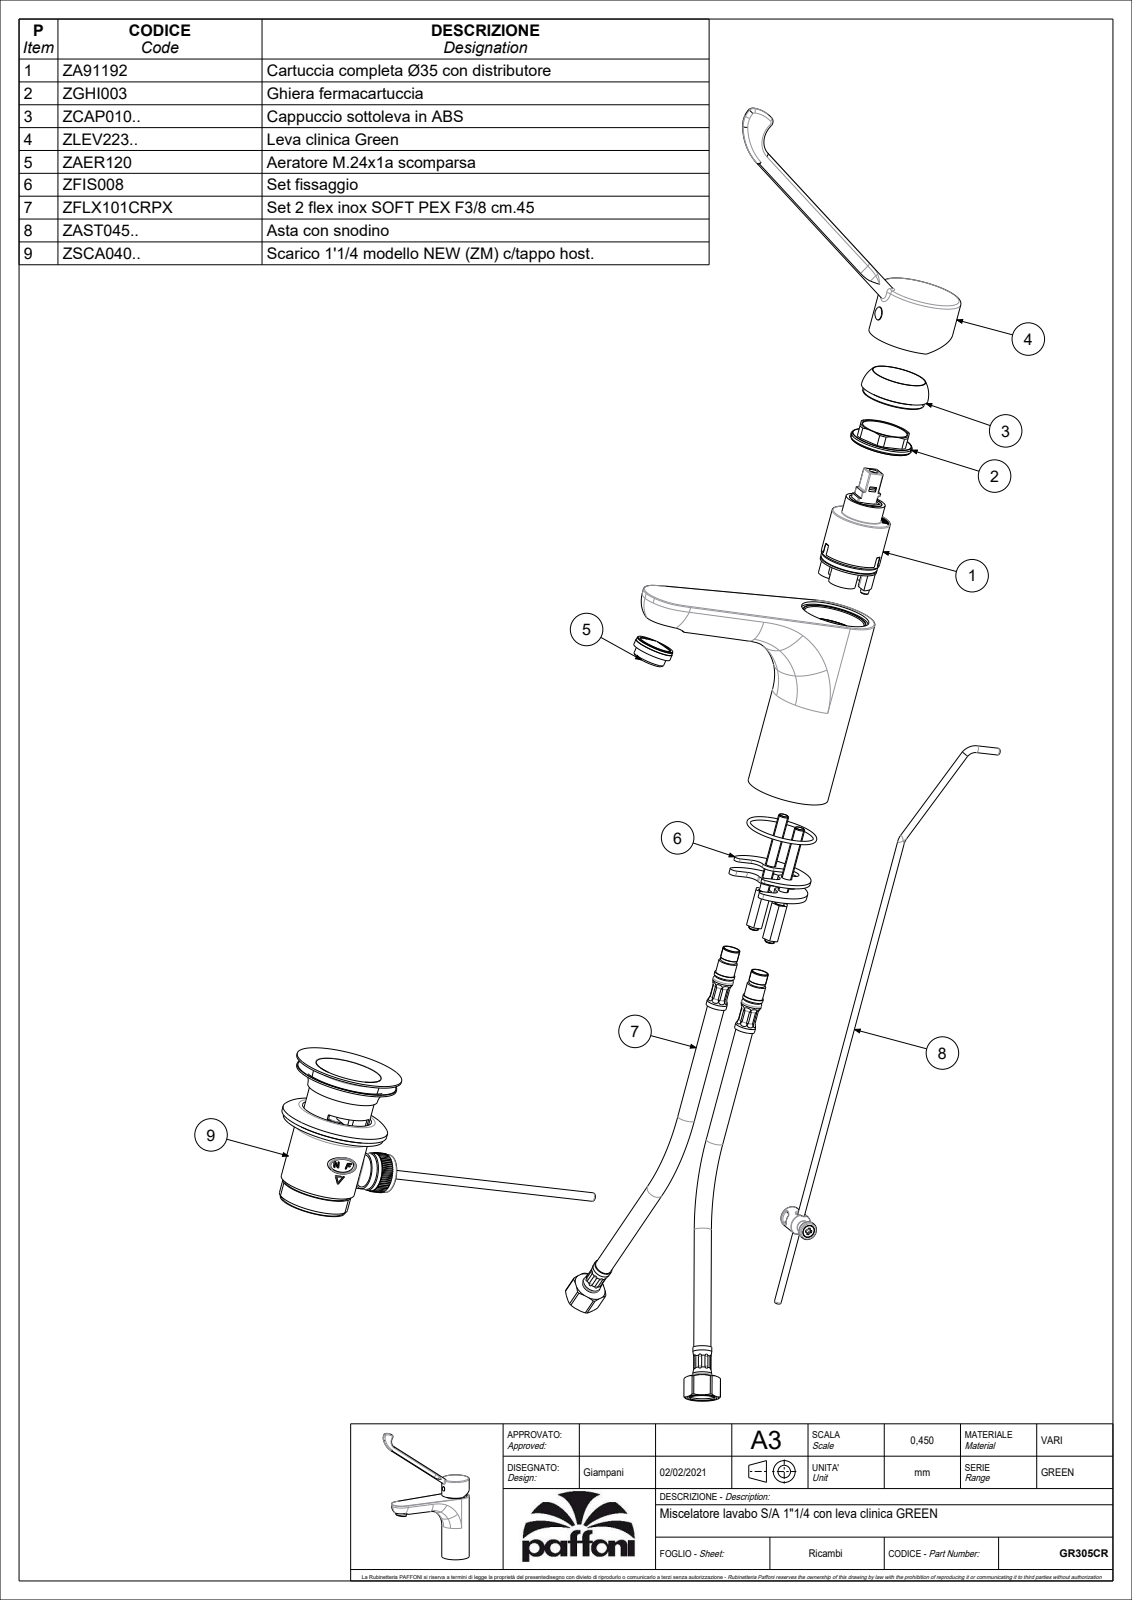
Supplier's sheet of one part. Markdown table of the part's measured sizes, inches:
| quantity | value |
| --- | --- |
| part name | GR305CR |
| STEP written by | CREO PARAMETRIC BY PTC INC, 2020044 (CONFIG_CONTROL_DESIGN) |
| units | inches |
| bodies | 5 solids, 1533 faces (554 planar, 499 cylindrical, 480 other) |
| overall size | 9.499 × 7.72 × 1.89 |
| volume | 9.164 in³ |
| surface area | 162.5 in² |
| round holes (diameter × count) | 0.197 × 5, 0.354 × 5, 0.177 × 3, 0.472 × 3, 0.236 × 2, 0.256 × 2, 0.315 × 2, 0.768 × 2, 0.984 × 2, 0.118 × 1, 0.13 × 1, 0.134 × 1 |
| round bosses / shafts (diameter × count) | 0.157 × 3, 0.441 × 2, 0.425 × 2, 0.394 × 2, 0.323 × 2, 0.189 × 2, 1.89 × 1, 1.516 × 1 |
| partial cylindrical surfaces (radius × count) | 0.02 × 103, 0.059 × 28, 0.039 × 22, 0.012 × 20, 0.05 × 14, 0.081 × 14, 0.236 × 8, 0.079 × 3 |
| main face-to-face distances | 0.098, 0.039, 0.177, 1.24, 1.339, 0.118, 1.063, 0.394, 0.354, 2.421 |
| hole center spacings | 0.535, 0.028, 0.111, 0.335, 0.339, 0.38, 0.388, 0.44 |
